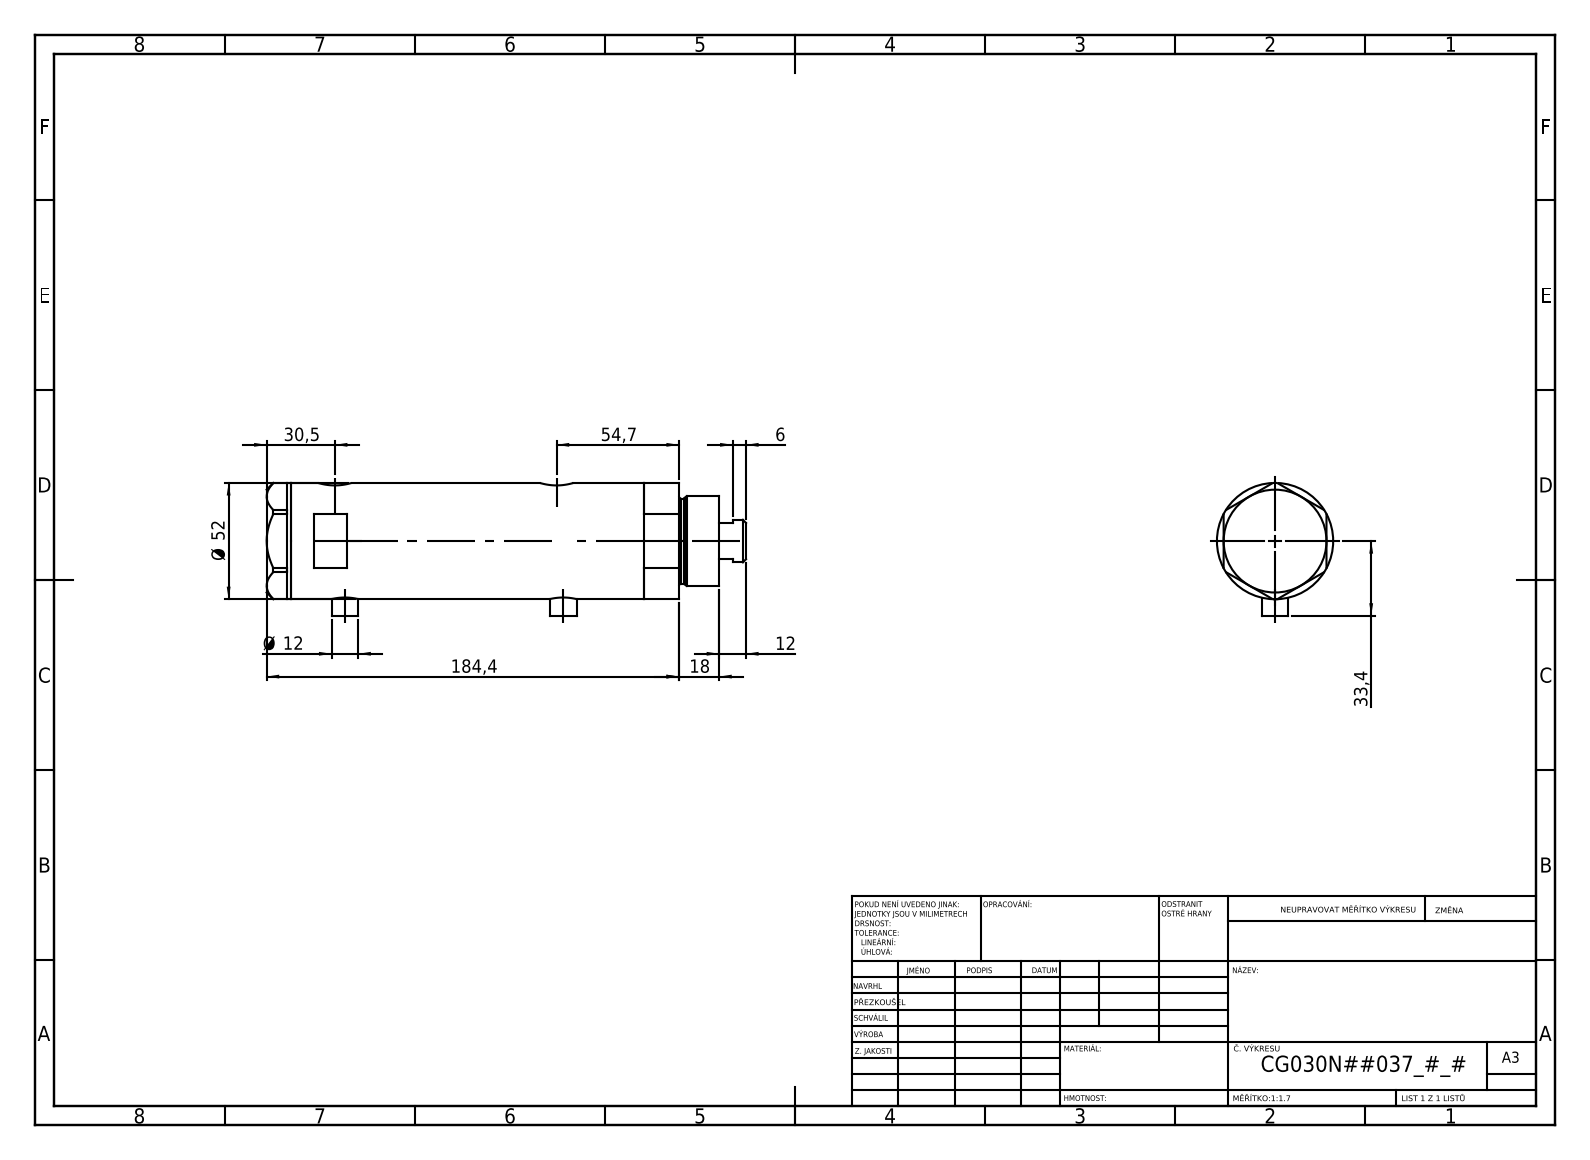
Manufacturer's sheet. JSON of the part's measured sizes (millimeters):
{"part_name": "V270CG_MIDDLE; V270CG_FRONT; V270CG_BACK; V270CG_VC", "step_written_by": "SolidWorks 2019 (CONFIG_CONTROL_DESIGN)", "units": "millimeters", "bodies": {"solids": 4, "faces": 134, "planar": 65, "cylindrical": 49, "other": 20}, "overall_size": [214.4, 59.4, 52], "volume_mm3": 395882, "surface_area_mm2": 87471, "round_holes": [[9.73, 2], [12.5, 2], [15, 2], [6.5, 1], [20, 1], [21.5, 1], [30, 1], [33, 1], [44, 1]], "round_bosses_or_shafts": [[12, 2], [52, 1], [40, 1], [38, 1], [19, 1]], "face_to_face_distances": [121.5, 23.8, 97.7, 11, 34.8, 132.5, 46, 168.9, 157.9, 134.1], "hole_center_spacings": [2.9, 4.5, 94.7, 97.6, 99.2, 102.1]}
